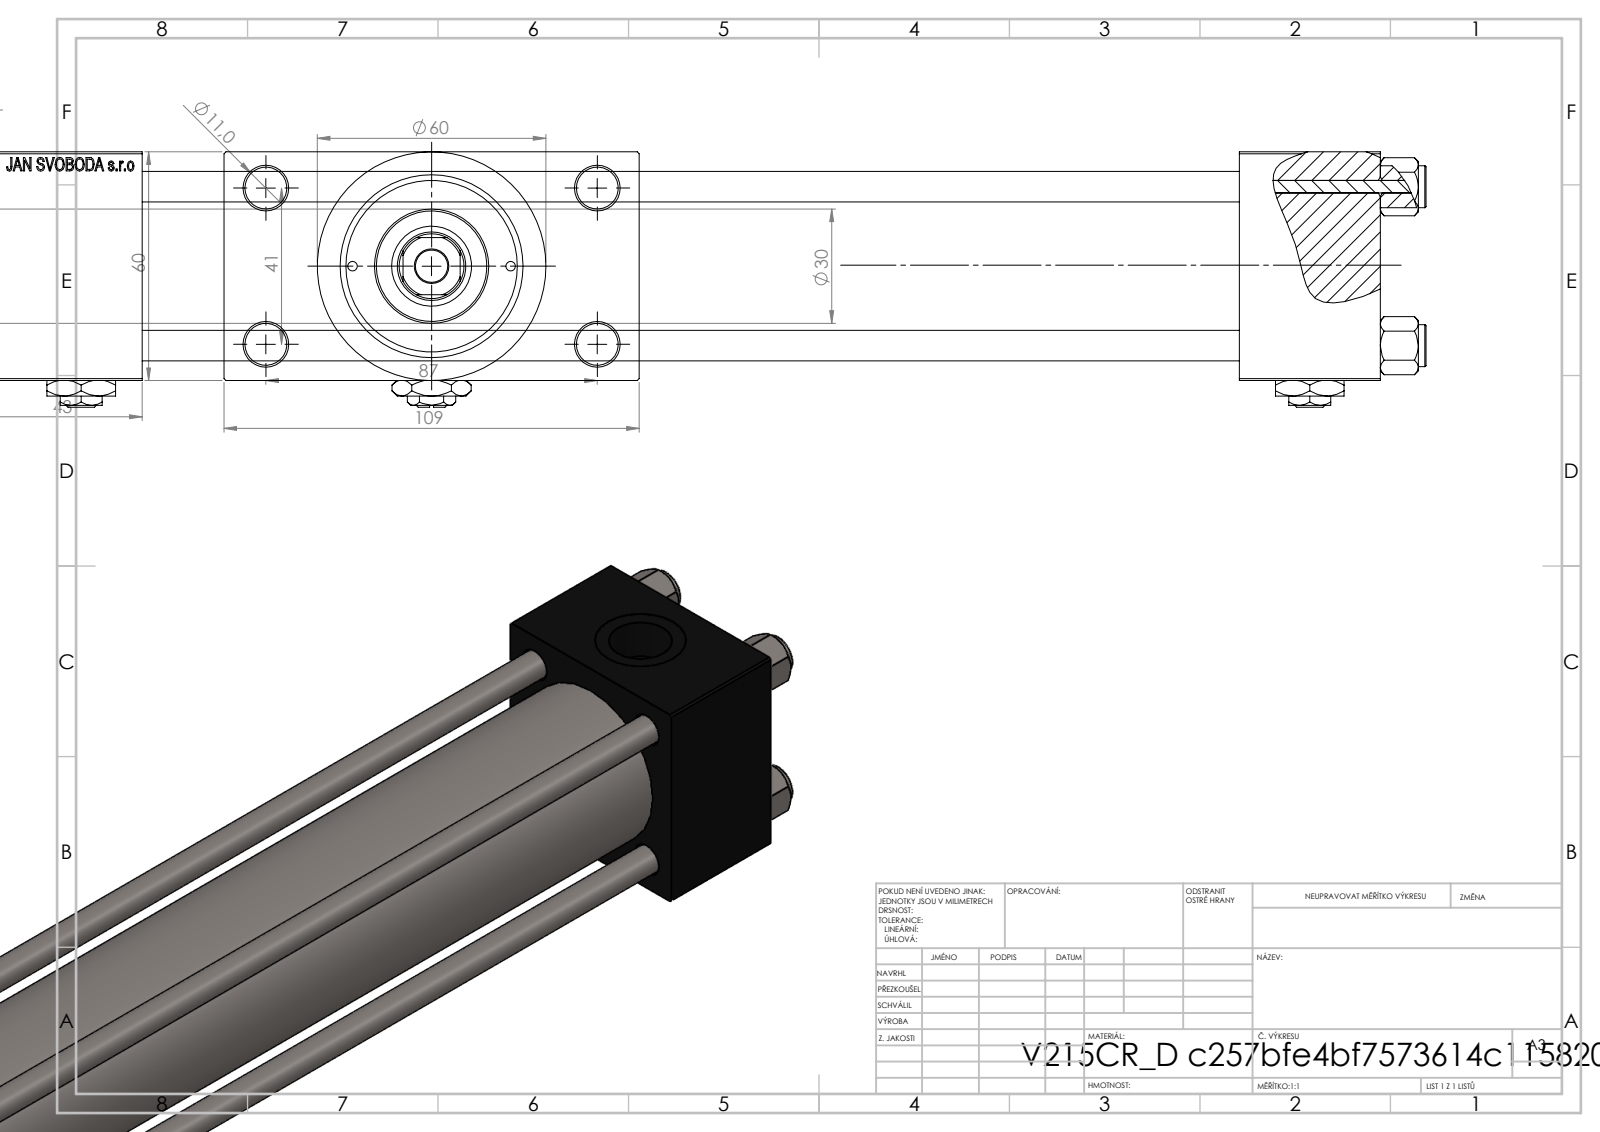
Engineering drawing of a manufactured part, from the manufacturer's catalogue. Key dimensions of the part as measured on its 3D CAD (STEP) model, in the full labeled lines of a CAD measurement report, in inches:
Part name (STEP PRODUCT): V215CR_D_TYCINKA; V215_VC_A; Zatka_pro_OIL_PORT; V215CR_VCP_D (+2 more)
STEP written by: SolidWorks 2019 (CONFIG_CONTROL_DESIGN)
Units: inches
Bodies: 13 solids, 1214 faces (548 planar, 104 cylindrical, 562 other)
Overall size (bounding box): 16.339 × 4.291 × 2.638
Volume: 43.53 in³ · Surface area: 344.3 in²
Round holes (diameter × count): ⌀0.315 ×4, ⌀0.433 ×4, ⌀0.098 ×2, ⌀0.276 ×2, ⌀0.656 ×2, ⌀0.945 ×2, ⌀0.335 ×1, ⌀0.709 ×1, ⌀0.827 ×1, ⌀1.22 ×1, ⌀1.575 ×1, ⌀1.772 ×1
Round bosses / shafts (diameter × count): ⌀0.433 ×4, ⌀2.362 ×1, ⌀1.811 ×1, ⌀1.181 ×1
Partial cylindrical surfaces — rounded edges, fillets, slot ends (radius × count): R0.335 ×1
Main face-to-face distances: 2.362, 0.965, 3.327, 11.339, 1.457, 12.795, 1.693, 14.488, 13.031, 4.291
Hole centre spacings: 0.821, 0.892, 1.161, 1.206, 1.642, 1.832, 1.856, 1.893
